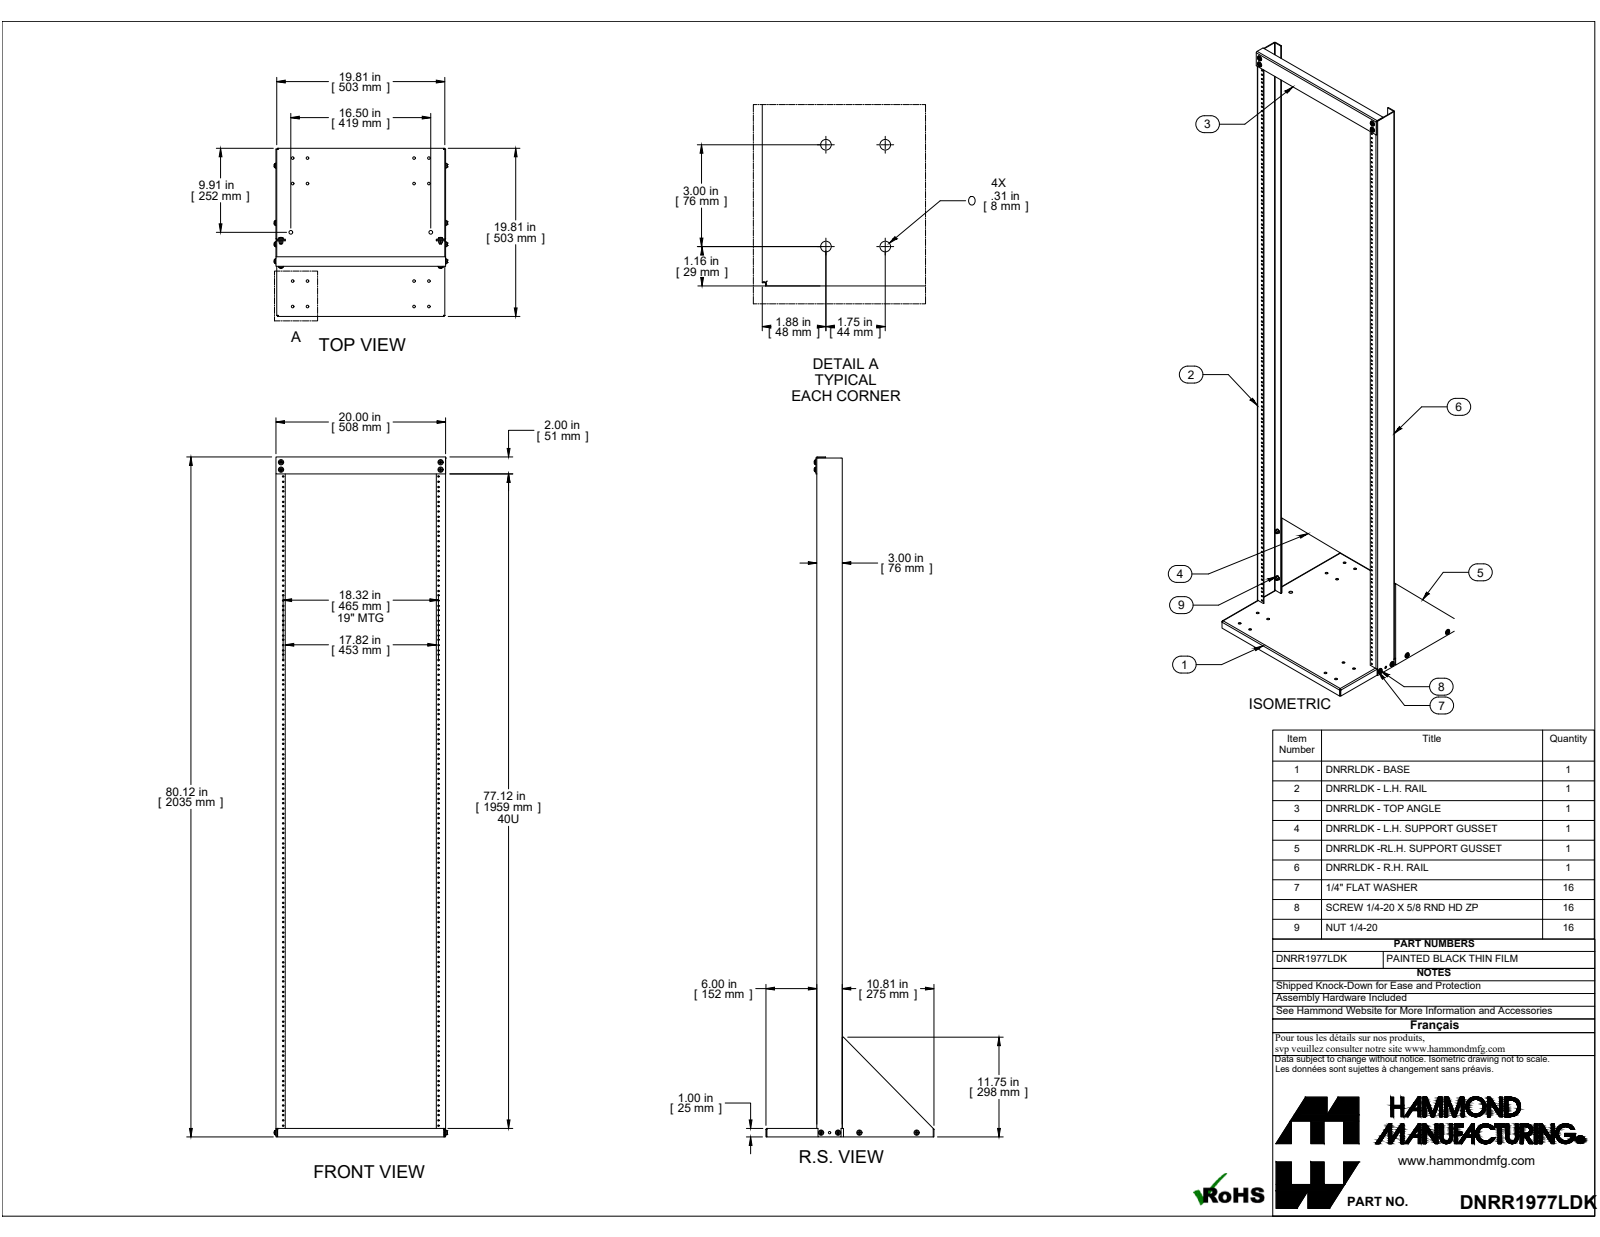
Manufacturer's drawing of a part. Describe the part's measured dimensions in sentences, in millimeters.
The part is named "DNRR1977LDK". Its 3-D file was written by "SolidWorks 2019 (CONFIG_CONTROL_DESIGN)". It is 54 solids with 1110 faces: 584 planar, 422 cylindrical and 104 other. Overall it measures 2035.2 by 518.1 by 503.2 millimeters. Its volume is 2 279 000 cubic millimeters and its surface area 1 941 000 square millimeters. Round holes: 264 of diameter 4.5, 18 of diameter 8, 15 of diameter 7.1, 12 of diameter 5, 12 of diameter 7.2, 2 of diameter 11.1. Round bosses or shafts: 12 of diameter 11.9, 12 of diameter 6.4, 8 of diameter 15.9, 4 of diameter 15.9. Partial cylindrical surfaces (rounded edges, fillets, slot ends): 11 of radius 1.2, 11 of radius 3.6, 4 of radius 4. The main face-to-face distances are 2.4, 2.4, 505.6, 503.2, 508.1, 76.2, 73.8, 71.4, 73.8, 4.8. The hole center spacings are 44.5, 88.9, 133.4, 76.2, 177.8, 222.3, 266.7, 15.9.
